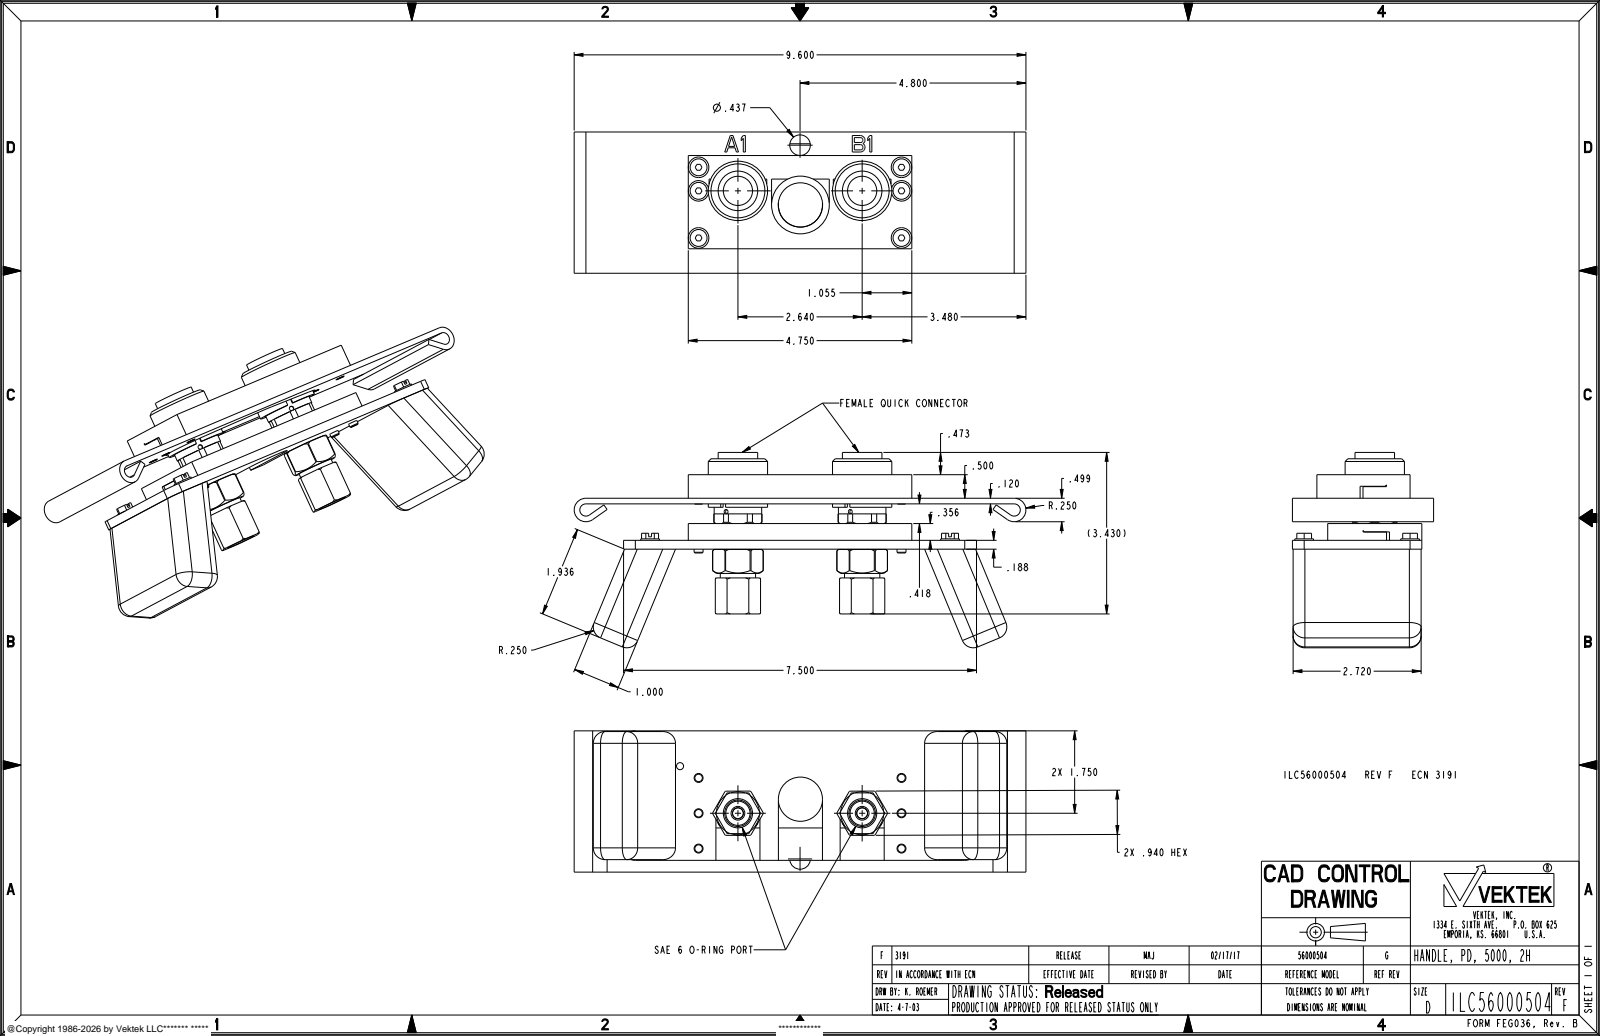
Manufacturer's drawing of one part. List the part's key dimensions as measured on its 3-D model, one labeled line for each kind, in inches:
Part name (STEP PRODUCT): ILC56000504
STEP written by: PRO/ENGINEER BY PARAMETRIC TECHNOLOGY CORPORATION, 2013320 (AUTOMOTIVE_DESIGN)
Units: inches
Bodies: 1 solid, 1046 faces (504 planar, 310 cylindrical, 232 other)
Overall size (bounding box): 9.6 × 4.149 × 3
Volume: 27.69 in³ · Surface area: 223.5 in²
Round holes (diameter × count): ⌀0.219 ×10, ⌀0.173 ×4, ⌀0.22 ×4, ⌀0.264 ×4, ⌀0.942 ×3, ⌀1.226 ×3, ⌀0.094 ×2, ⌀0.228 ×2, ⌀0.292 ×2, ⌀0.43 ×2, ⌀0.509 ×2, ⌀0.515 ×2
Round bosses / shafts (diameter × count): ⌀0.19 ×14, ⌀0.159 ×10, ⌀0.396 ×4, ⌀1.26 ×2, ⌀1.01 ×2, ⌀0.923 ×2, ⌀0.84 ×2, ⌀0.75 ×2
Partial cylindrical surfaces — rounded edges, fillets, slot ends (radius × count): R0.25 ×20, R0.468 ×3, R0.68 ×3, R0.059 ×2, R0.13 ×2, R0.25 ×2, R0.511 ×2, R0.537 ×2
Main face-to-face distances: 0.12, 0.894, 0.774, 1.081, 0.962, 0.188, 1, 0.5, 0.538, 0.418
Hole centre spacings: 4.312, 0.25, 0.75, 1.123, 1.275, 1.5, 1.82, 2.25
